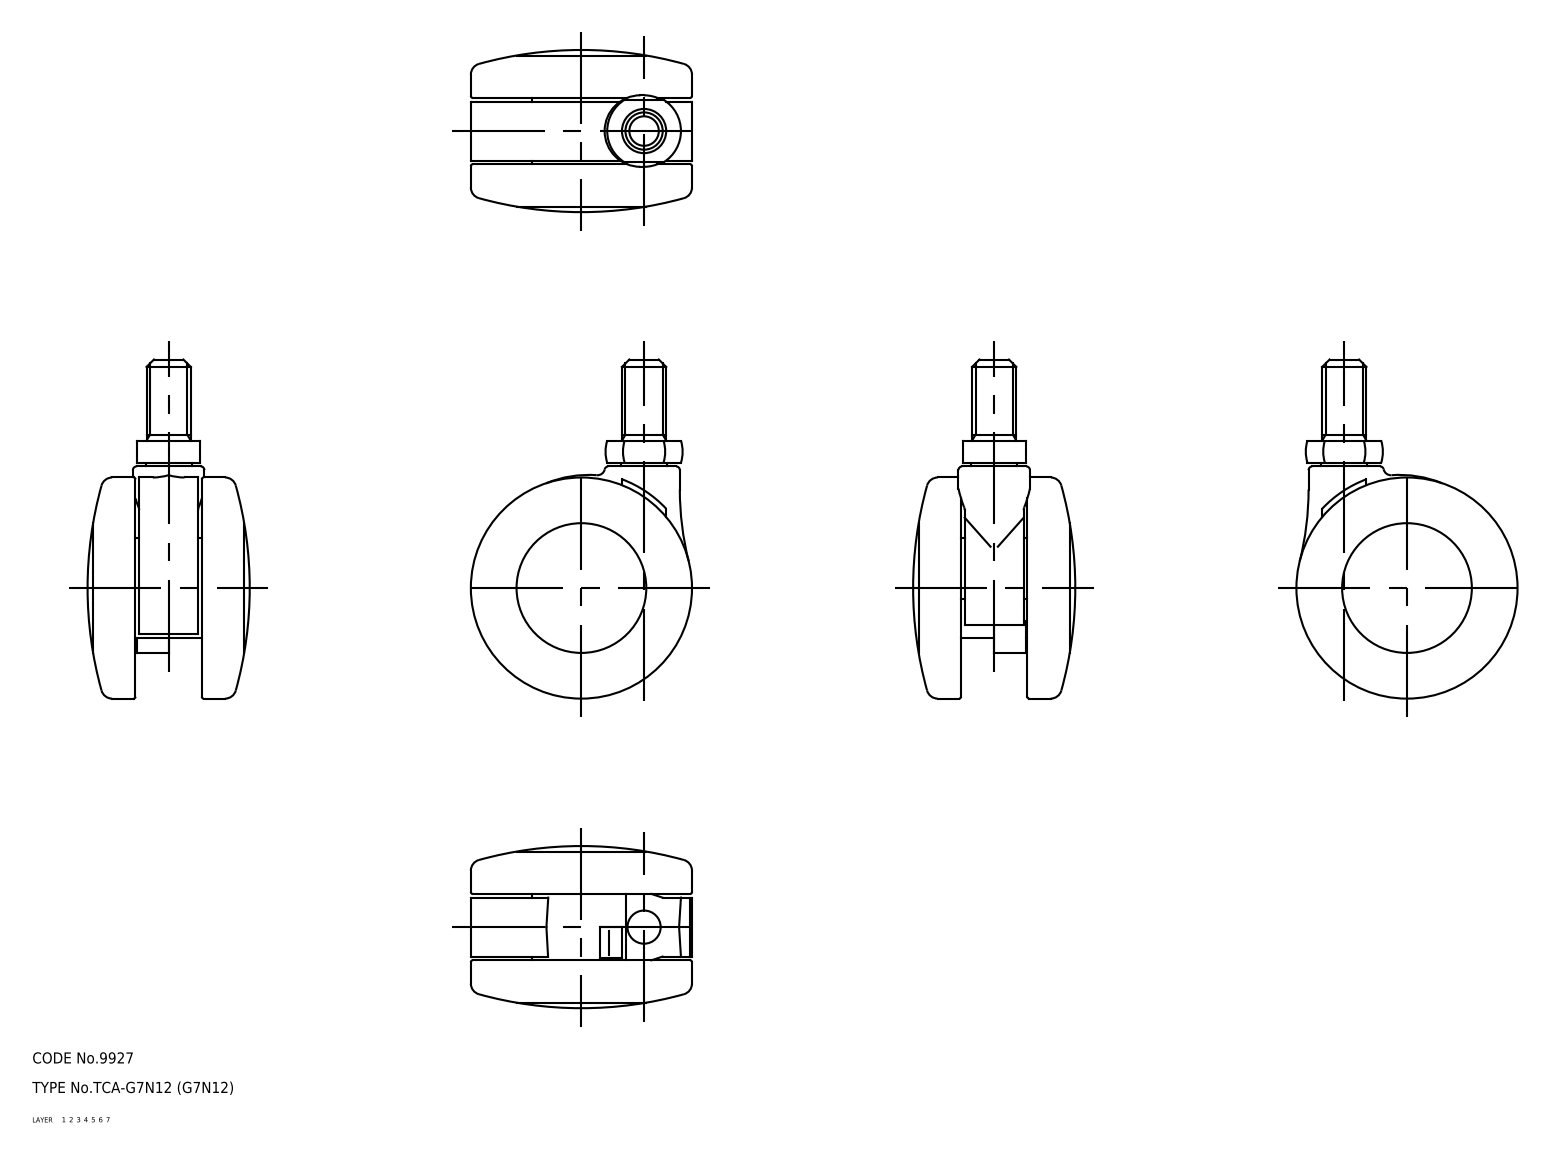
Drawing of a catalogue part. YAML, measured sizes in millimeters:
part_name: "wheel; main shaft; G7N12_13050_36"
step_written_by: "CADfix (AUTOMOTIVE_DESIGN)"
units: millimeters
bodies: {solids: 4, faces: 129, planar: 0, cylindrical: 0, other: 129}
overall_size: [92, 60, 44]
volume: 93735
surface_area: 33050
